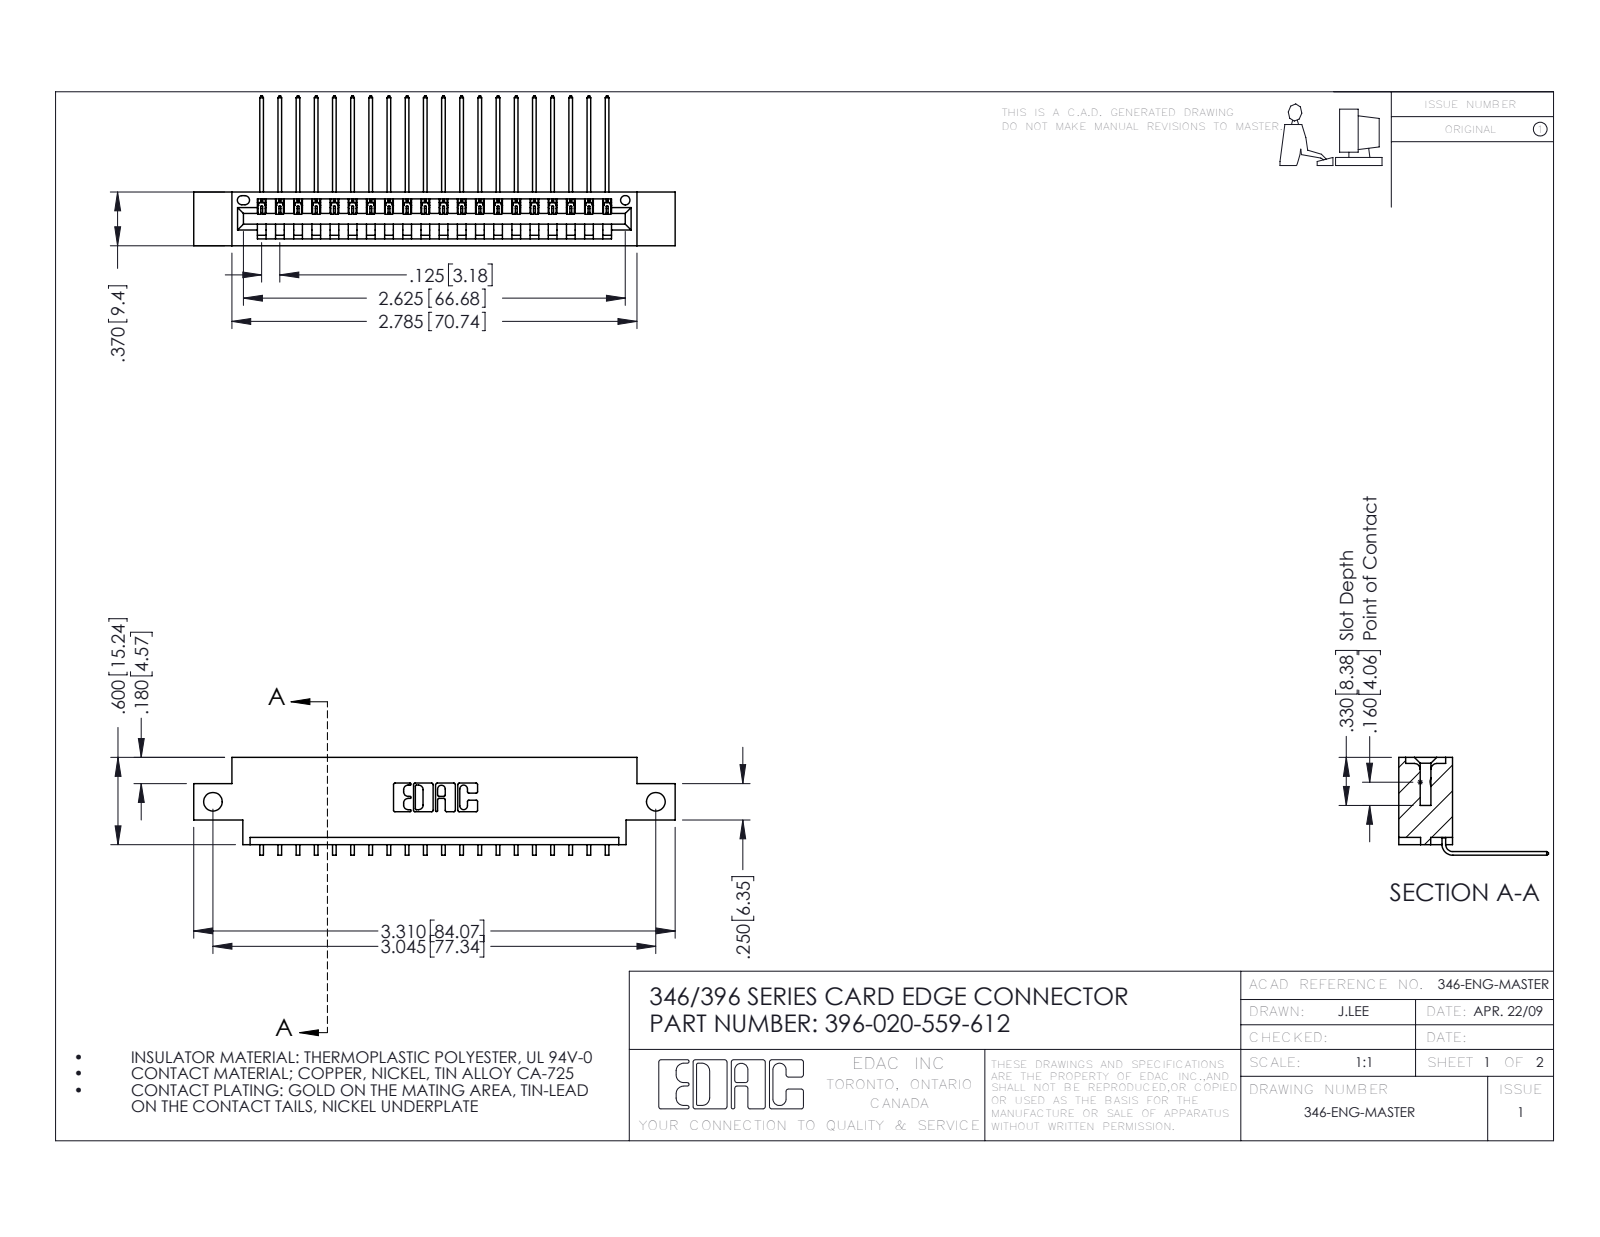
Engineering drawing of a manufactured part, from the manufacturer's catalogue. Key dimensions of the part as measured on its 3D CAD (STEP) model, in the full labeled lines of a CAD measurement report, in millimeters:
Part name (STEP PRODUCT): 345-292-001_558 559 Tail - 1; 346 Part_0.170 Offset - Side Mount; 396-020-559-612
STEP written by: SolidWorks 2016 (CONFIG_CONTROL_DESIGN)
Units: millimetres
Bodies: 21 solids, 1326 faces (920 planar, 406 cylindrical, 0 other)
Overall size (bounding box): 84.1 × 26.2 × 17.1
Volume: 7 720 mm³ · Surface area: 9 826 mm²
Round holes (diameter × count): ⌀3.3 ×2, ⌀1.6 ×1
Partial cylindrical surfaces — rounded edges, fillets, slot ends (radius × count): R0.2 ×40, R0.3 ×22, R0.2 ×6, R0.8 ×6, R0.7 ×3, R0.8 ×2, R1 ×2, R0.4 ×1
Main face-to-face distances: 1.2, 9.4, 8.2, 6.4, 0.6, 1.8, 3.8, 5.6, 2.5, 4.4
Hole centre spacings: 77.3
